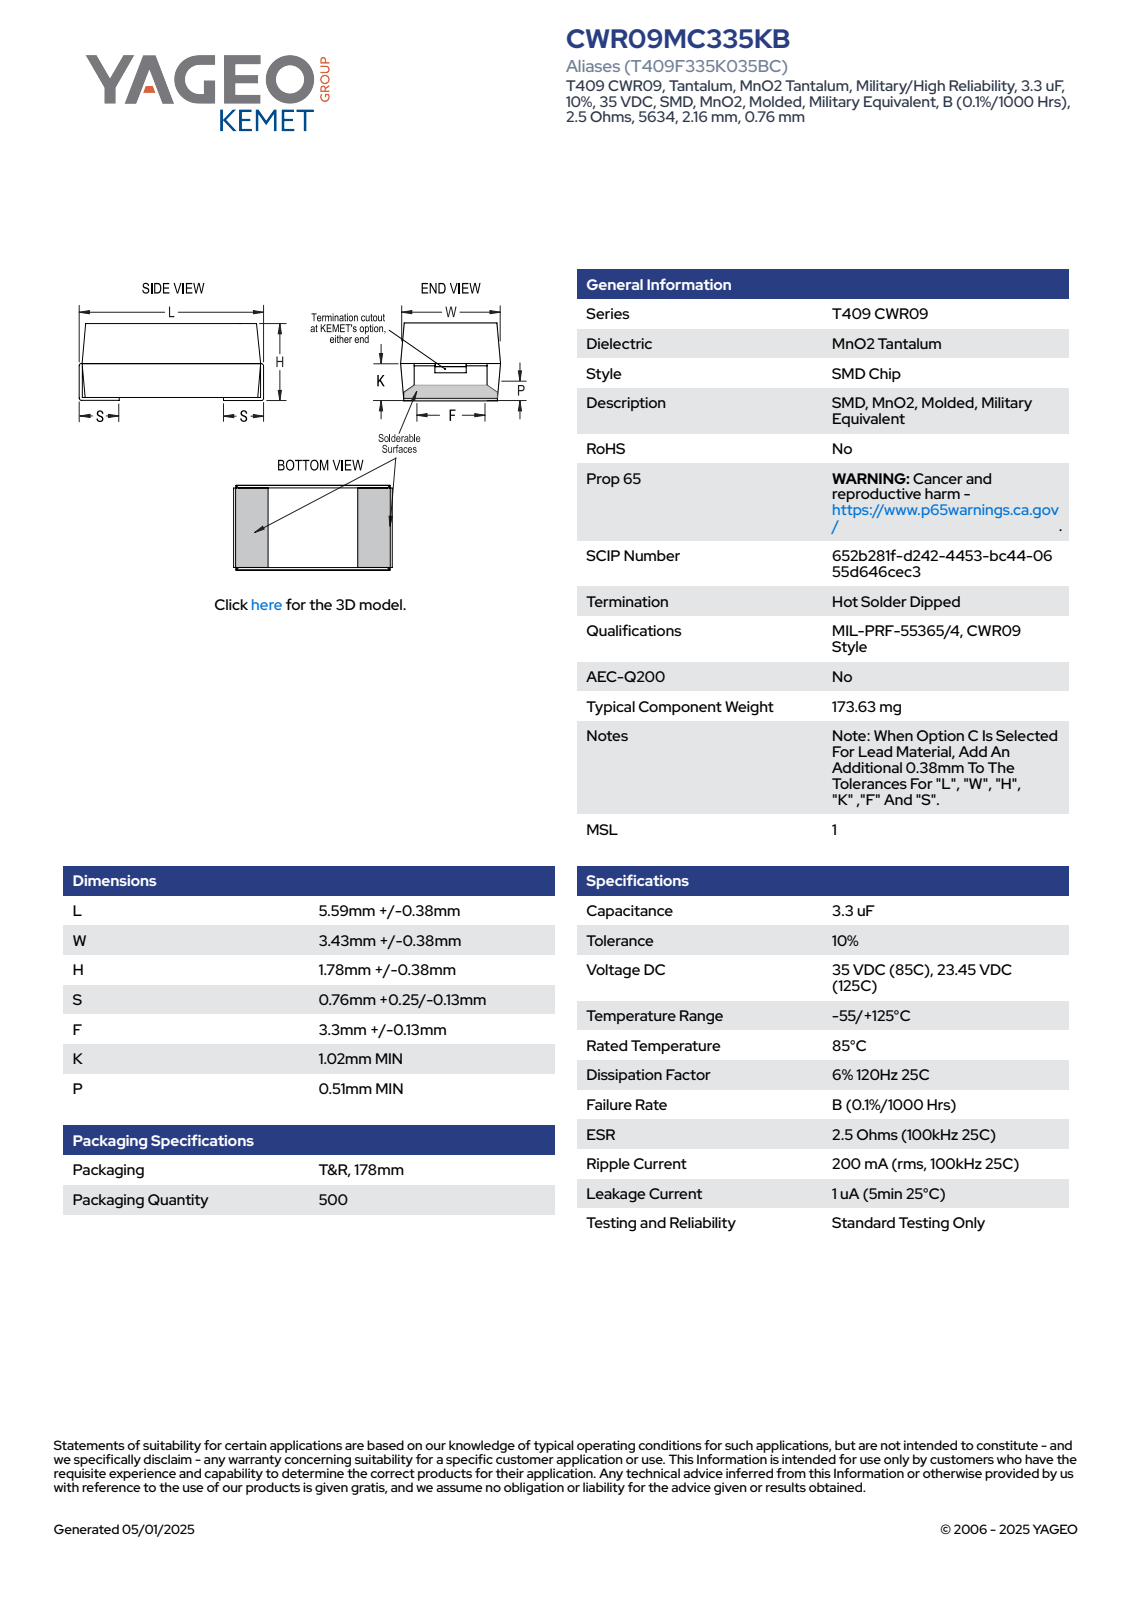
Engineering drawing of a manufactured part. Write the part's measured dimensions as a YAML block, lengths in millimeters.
part_name: "CTS_TCM3M_5634_L5.97H2.16S0.76F3.43K1.02P0.51W3.81"
step_written_by: "SolidWorks 2014 (AUTOMOTIVE_DESIGN)"
units: millimeters
bodies: {solids: 4, faces: 85, planar: 81, cylindrical: 4, other: 0}
overall_size: [5.97, 3.81, 2.26]
volume: 45
surface_area: 98
partial_cylinders:
  - {radius: 0.1, count: 4}
face_to_face_distances: [2.16, 5.87, 2.26, 5.77, 5.97, 0.76, 5.21, 0.66, 5.11, 3.43]
